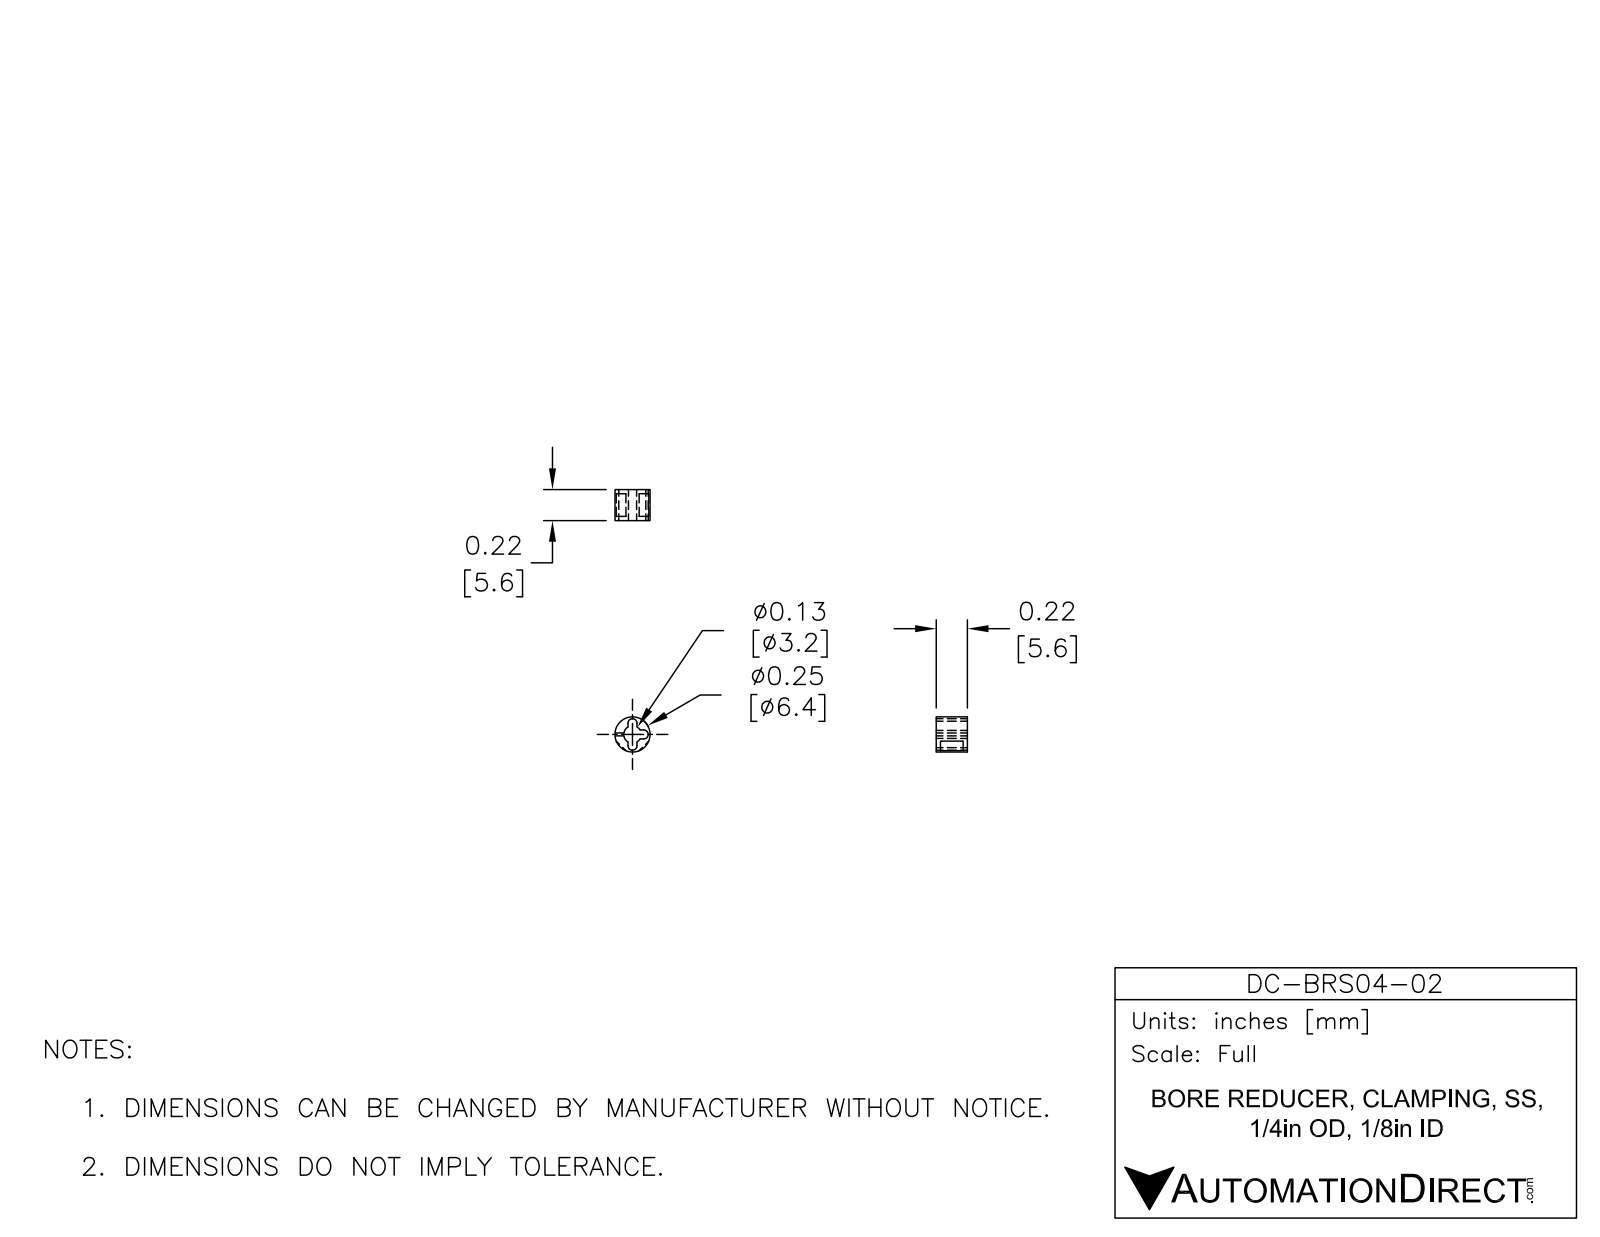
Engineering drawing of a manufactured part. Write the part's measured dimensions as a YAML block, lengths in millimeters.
part_name: "DC-BRS04-02"
step_written_by: "SolidWorks 2015 (AUTOMOTIVE_DESIGN)"
units: millimeters
bodies: {solids: 1, faces: 27, planar: 16, cylindrical: 11, other: 0}
overall_size: [6.35, 6.34, 5.61]
volume: 94
surface_area: 253
round_bosses_or_shafts:
  - {diameter: 6.35, count: 1}
partial_cylinders:
  - {radius: 0.81, count: 3}
  - {radius: 1.59, count: 1}
face_to_face_distances: [5.62, 1.62, 0.5, 0.56, 1.06, 0.77, 4.85, 4.08]
